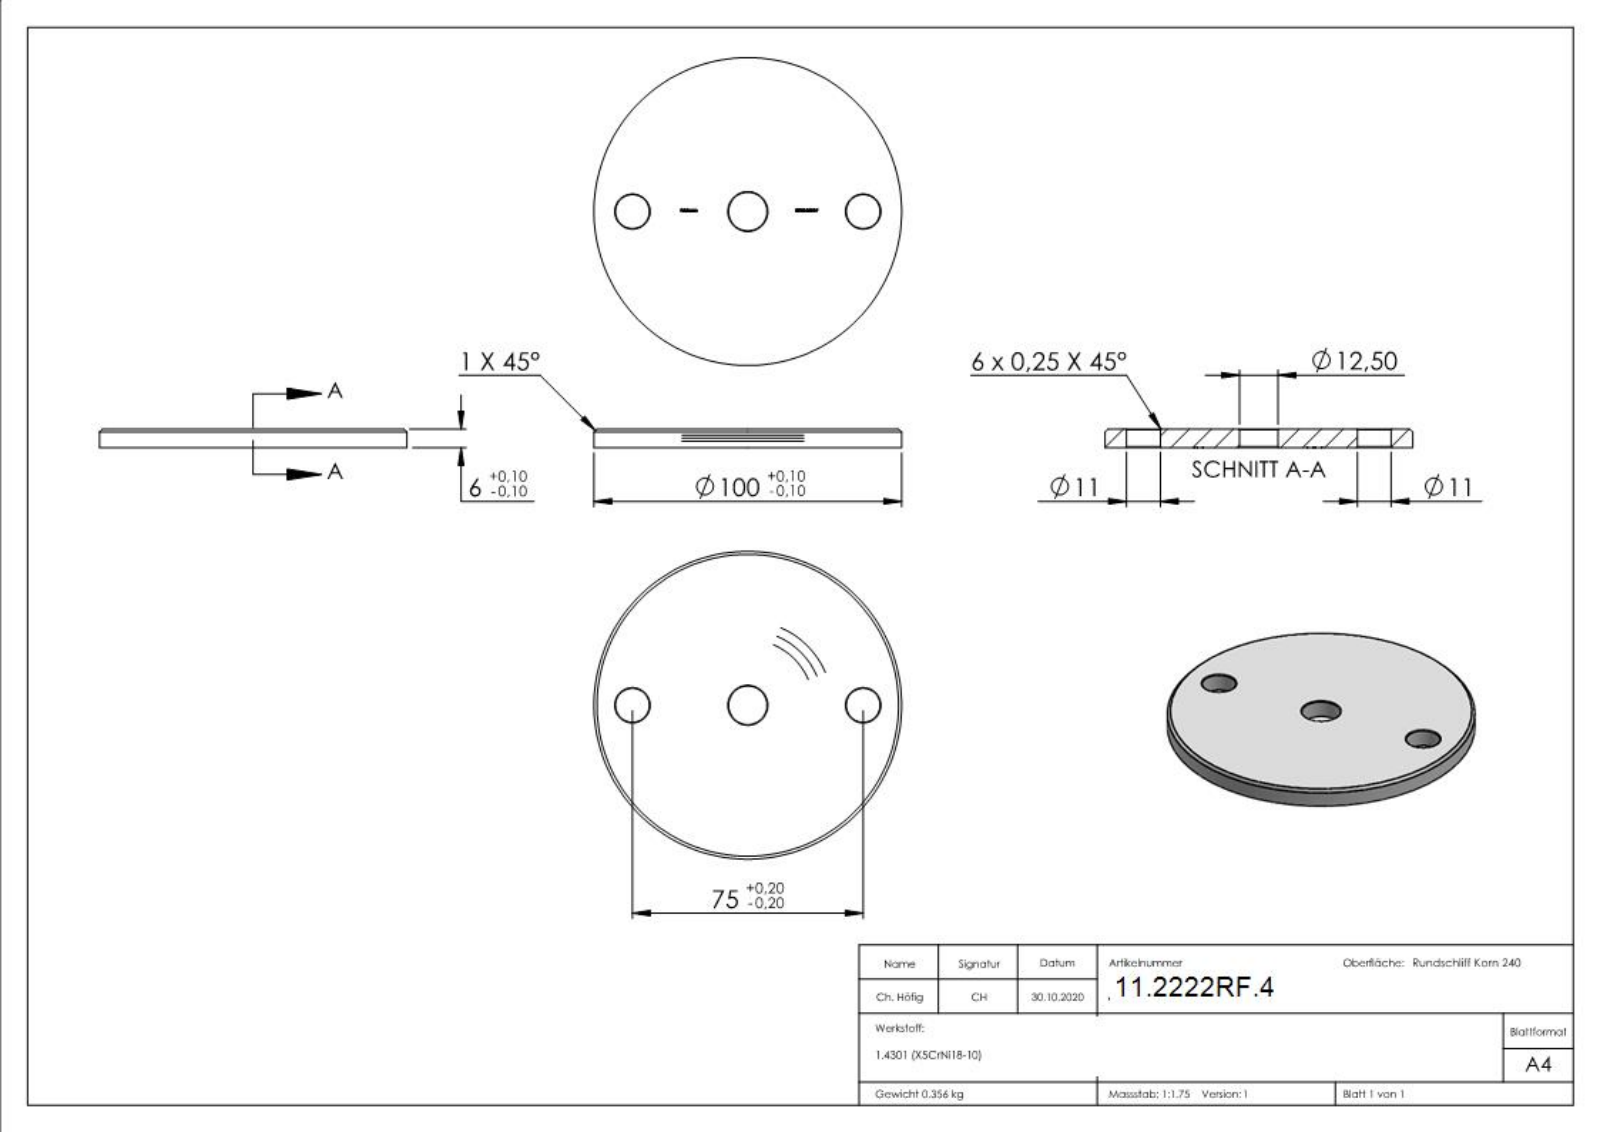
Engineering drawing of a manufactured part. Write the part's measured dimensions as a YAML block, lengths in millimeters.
part_name: "54100-240-R-F"
step_written_by: "SolidWorks 2018 (CONFIG_CONTROL_DESIGN)"
units: millimeters
bodies: {solids: 1, faces: 279, planar: 163, cylindrical: 8, other: 108}
overall_size: [100, 100, 6]
volume: 45084
surface_area: 17408
round_holes:
  - {diameter: 11, count: 2}
  - {diameter: 12.5, count: 1}
round_bosses_or_shafts:
  - {diameter: 100, count: 1}
face_to_face_distances: [6, 5.9, 0.53, 1.21, 41.73, 1.28, 41.66, 0.44, 0.32, 0.71]
hole_center_spacings: [37.5, 75]
